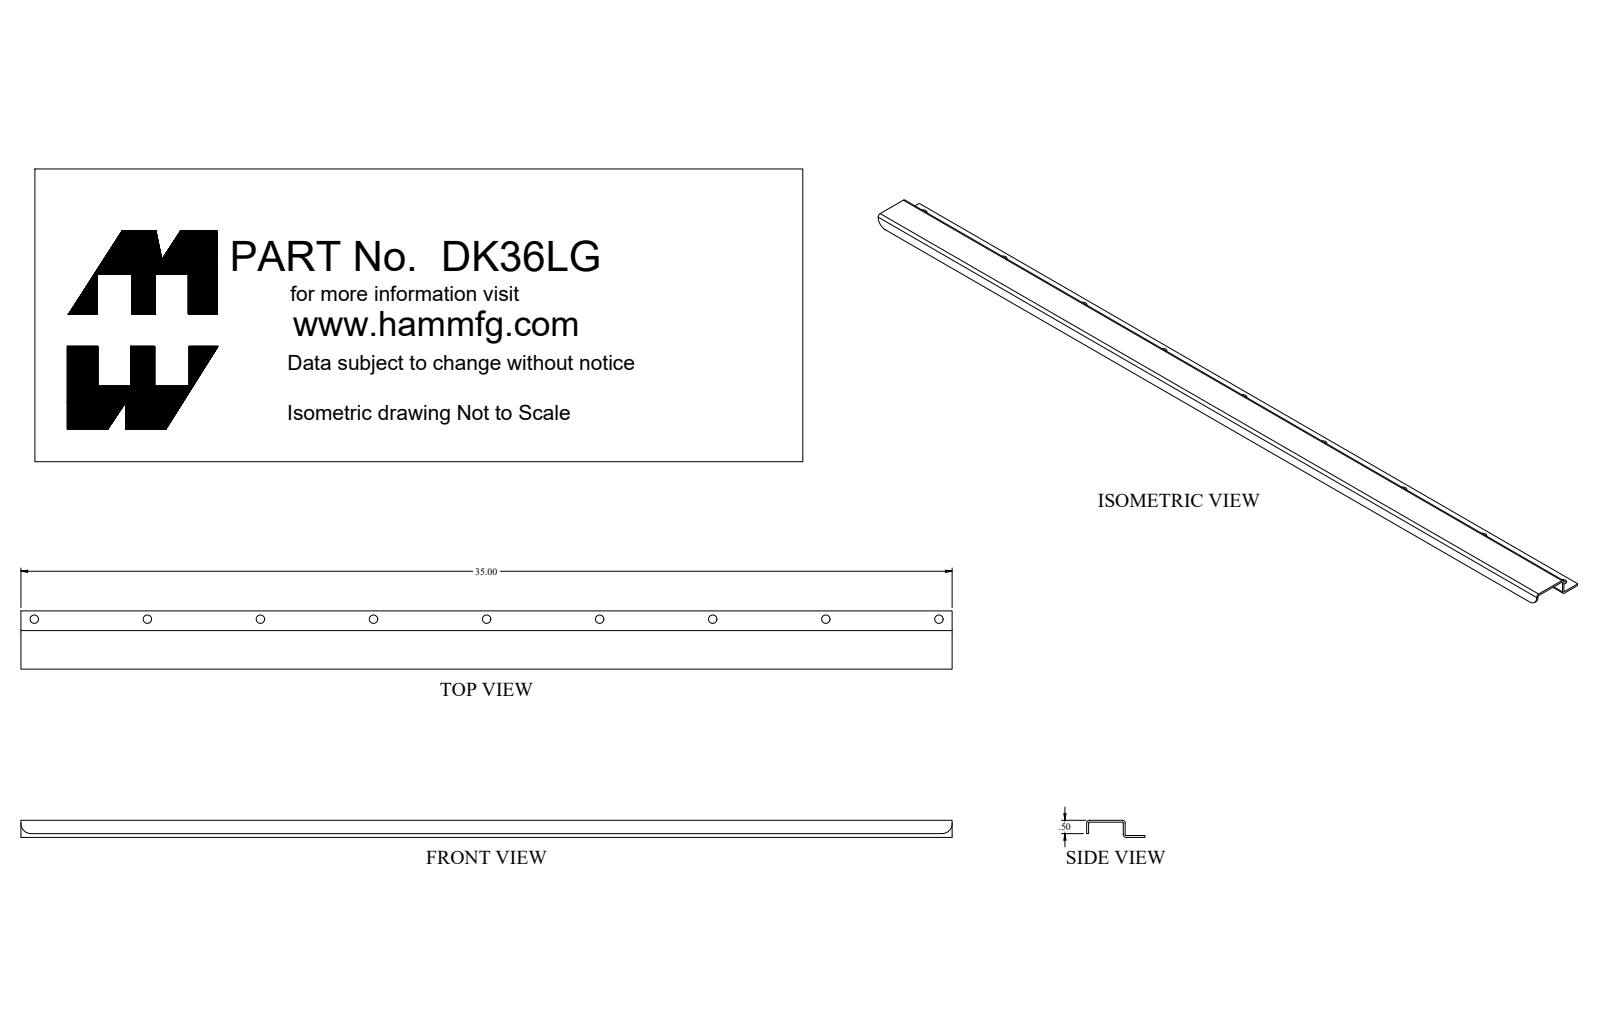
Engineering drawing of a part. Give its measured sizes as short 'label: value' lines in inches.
name: DK36LG_Default
written by: SolidWorks 2018 (CONFIG_CONTROL_DESIGN)
unit: in
bodies: 5 solids, 77 faces (35 planar, 36 cylindrical, 6 other)
size: 35 × 2.188 × 1.322
volume: 9.511 in³; area: 280.9 in²
holes: 9× ⌀0.313, 1× ⌀0.201, 1× ⌀0.275
bosses: 1× ⌀0.625, 1× ⌀0.483, 1× ⌀0.25
rounds: 3× R0.036, 3× R0.108, 2× R0.375
face distances: 0.072, 0.572, 0.644, 1.376, 0.5, 0.063, 0.635, 0.707, 0.135, 1.448
hole spacings: 4.25, 8.5, 12.75, 17, 21.25, 25.5, 29.75, 34
